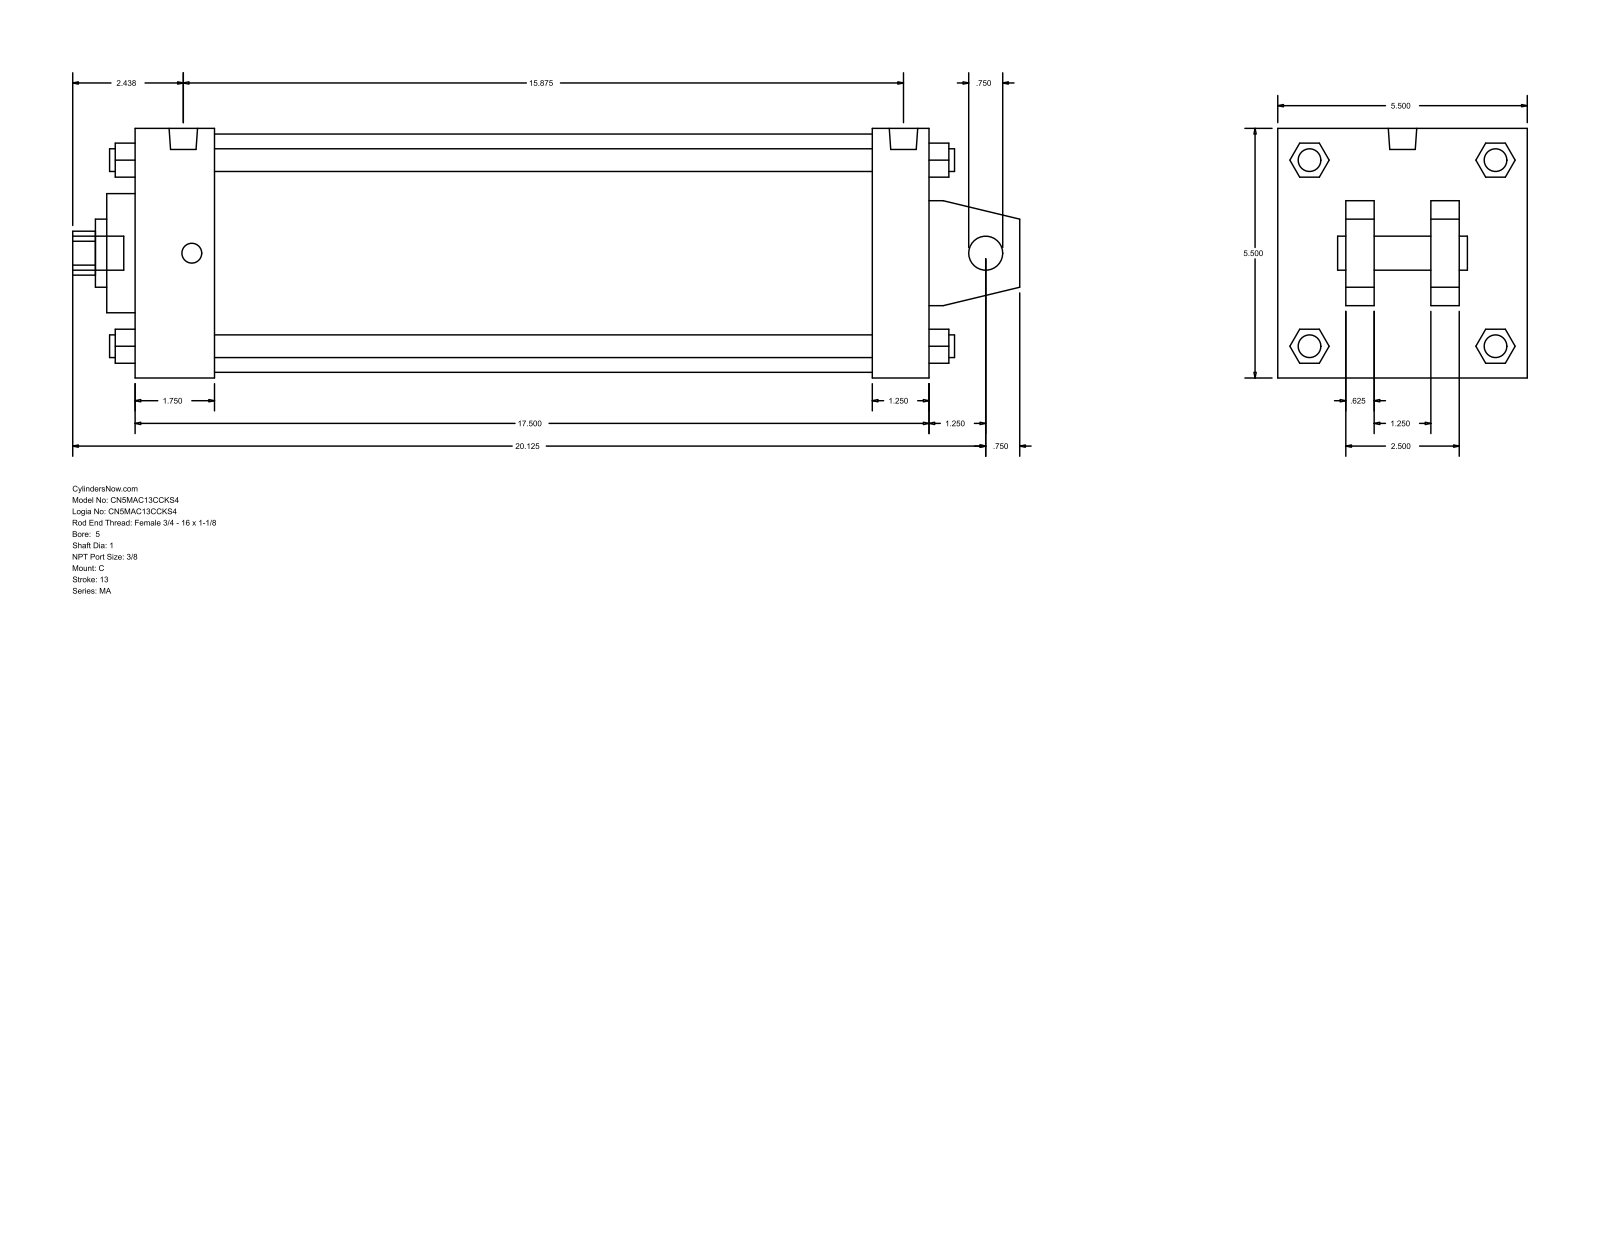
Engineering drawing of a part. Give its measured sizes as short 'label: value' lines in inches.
name: MA_C__0500_1
written by: GSSL Pune (CONFIG_CONTROL_DESIGN)
unit: in
bodies: 0 solids, 141 faces (109 planar, 32 cylindrical, 0 other)
size: 20.875 × 5.5 × 5.5
holes: 1× ⌀0.75, 1× ⌀1, 1× ⌀1.5, 1× ⌀2.625, 1× ⌀5.25
bosses: 4× ⌀0.5, 4× ⌀0.437, 2× ⌀0.627, 1× ⌀0.75
rounds: 1× R0.484
face distances: 5.5, 17.5, 0.625, 16.25, 1.25, 1.75, 14.5, 15.75, 1.5, 4
